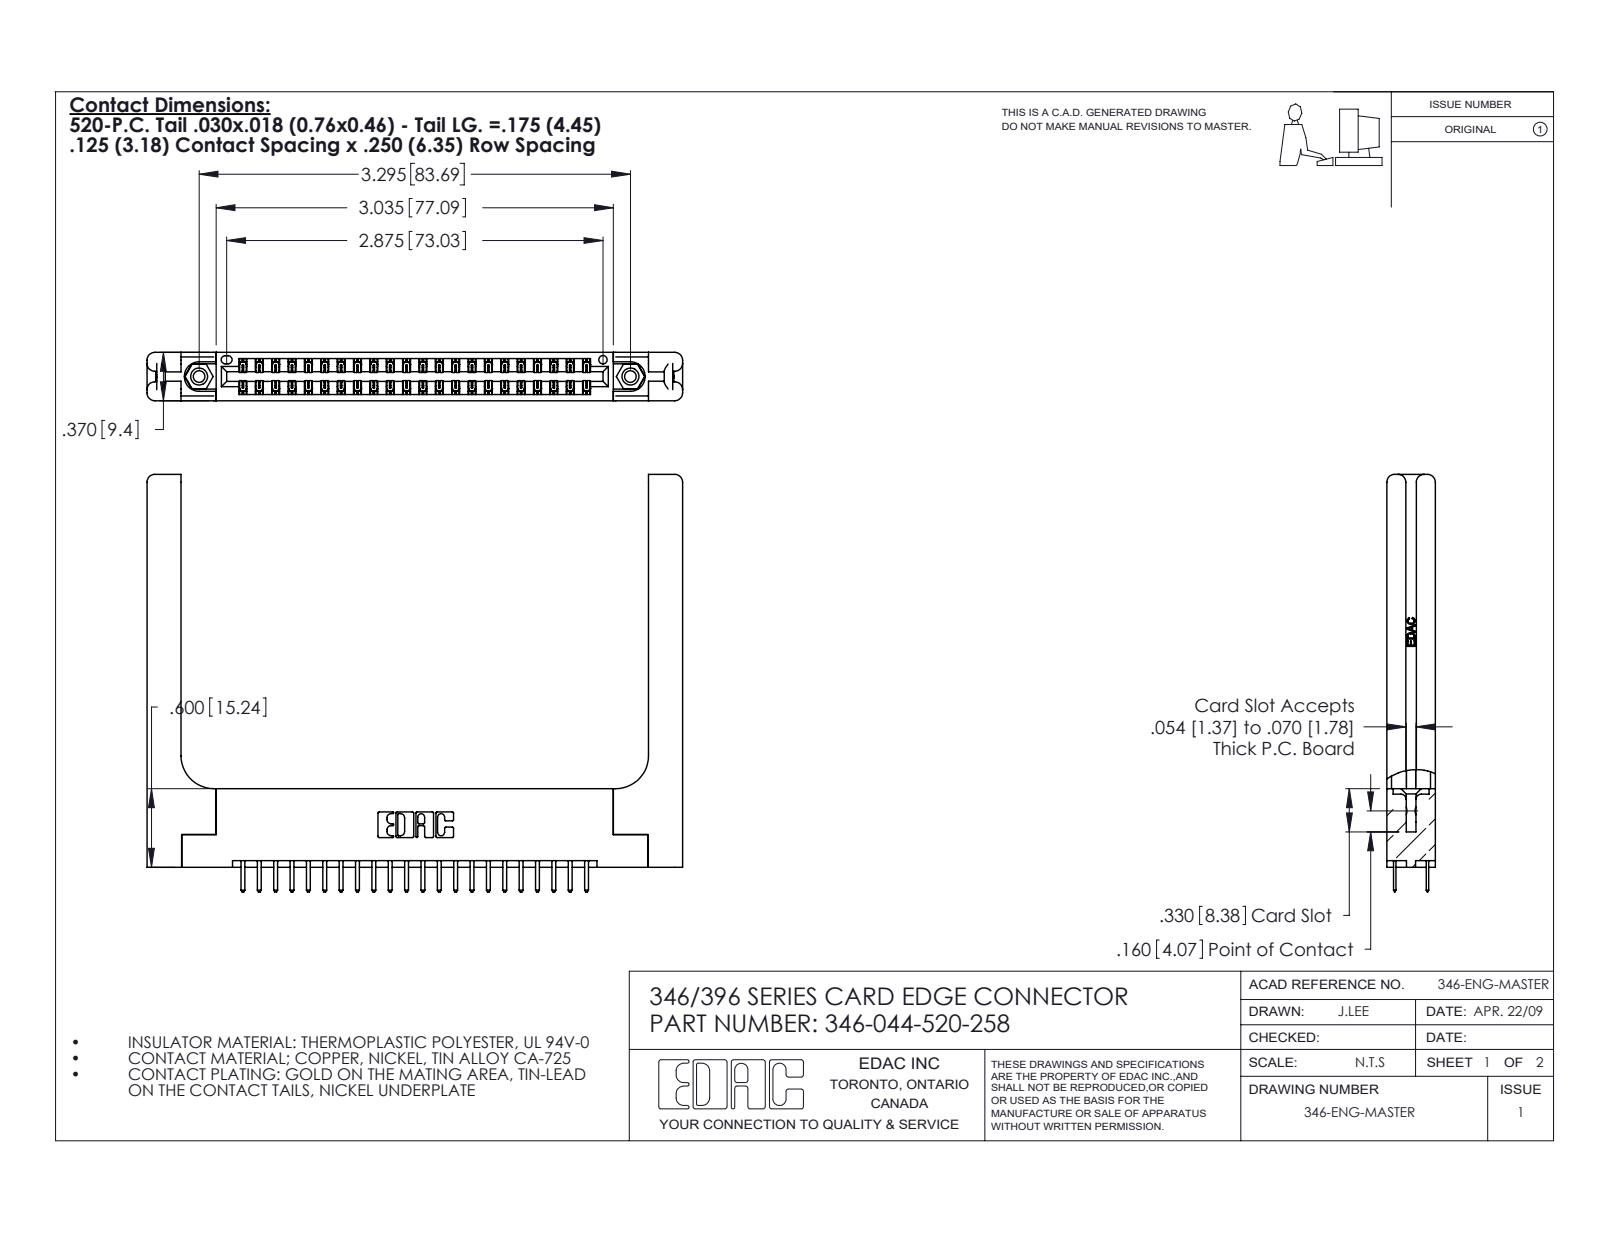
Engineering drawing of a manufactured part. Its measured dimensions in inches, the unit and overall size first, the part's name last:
Units: inches
Overall size (bounding box): 4.091 × 3.188 × 0.37
Round holes (diameter × count): ⌀0.089 ×2, ⌀0.125 ×2, ⌀0.156 ×2, ⌀0.064 ×1
Round bosses / shafts (diameter × count): ⌀0.155 ×2
Partial cylindrical surfaces — rounded edges, fillets, slot ends (radius × count): R0.006 ×66, R0.01 ×48, R0.01 ×22, R0.06 ×16, R0.007 ×6, R0.031 ×6, R0.026 ×3, R0.014 ×2
Main face-to-face distances: 0.37, 0.072, 0.148, 0.15, 0.048, 0.322, 0.25, 0.077, 0.298, 0.025
Hole centre spacings: 0.246, 3.087, 3.295
Volume: 1.064 in³ · Surface area: 28.38 in²
Bodies: 49 solids, 2856 faces (1866 planar, 930 cylindrical, 60 other)
Part name (STEP PRODUCT): 346-220-058_345-220-058; 345-292-001_345-293-120; 346-044-520-258; 346 Part_Flush Mounting Lugs - 0.156 Dia-TH (+1 more)
STEP written by: SolidWorks 2020 (CONFIG_CONTROL_DESIGN)
